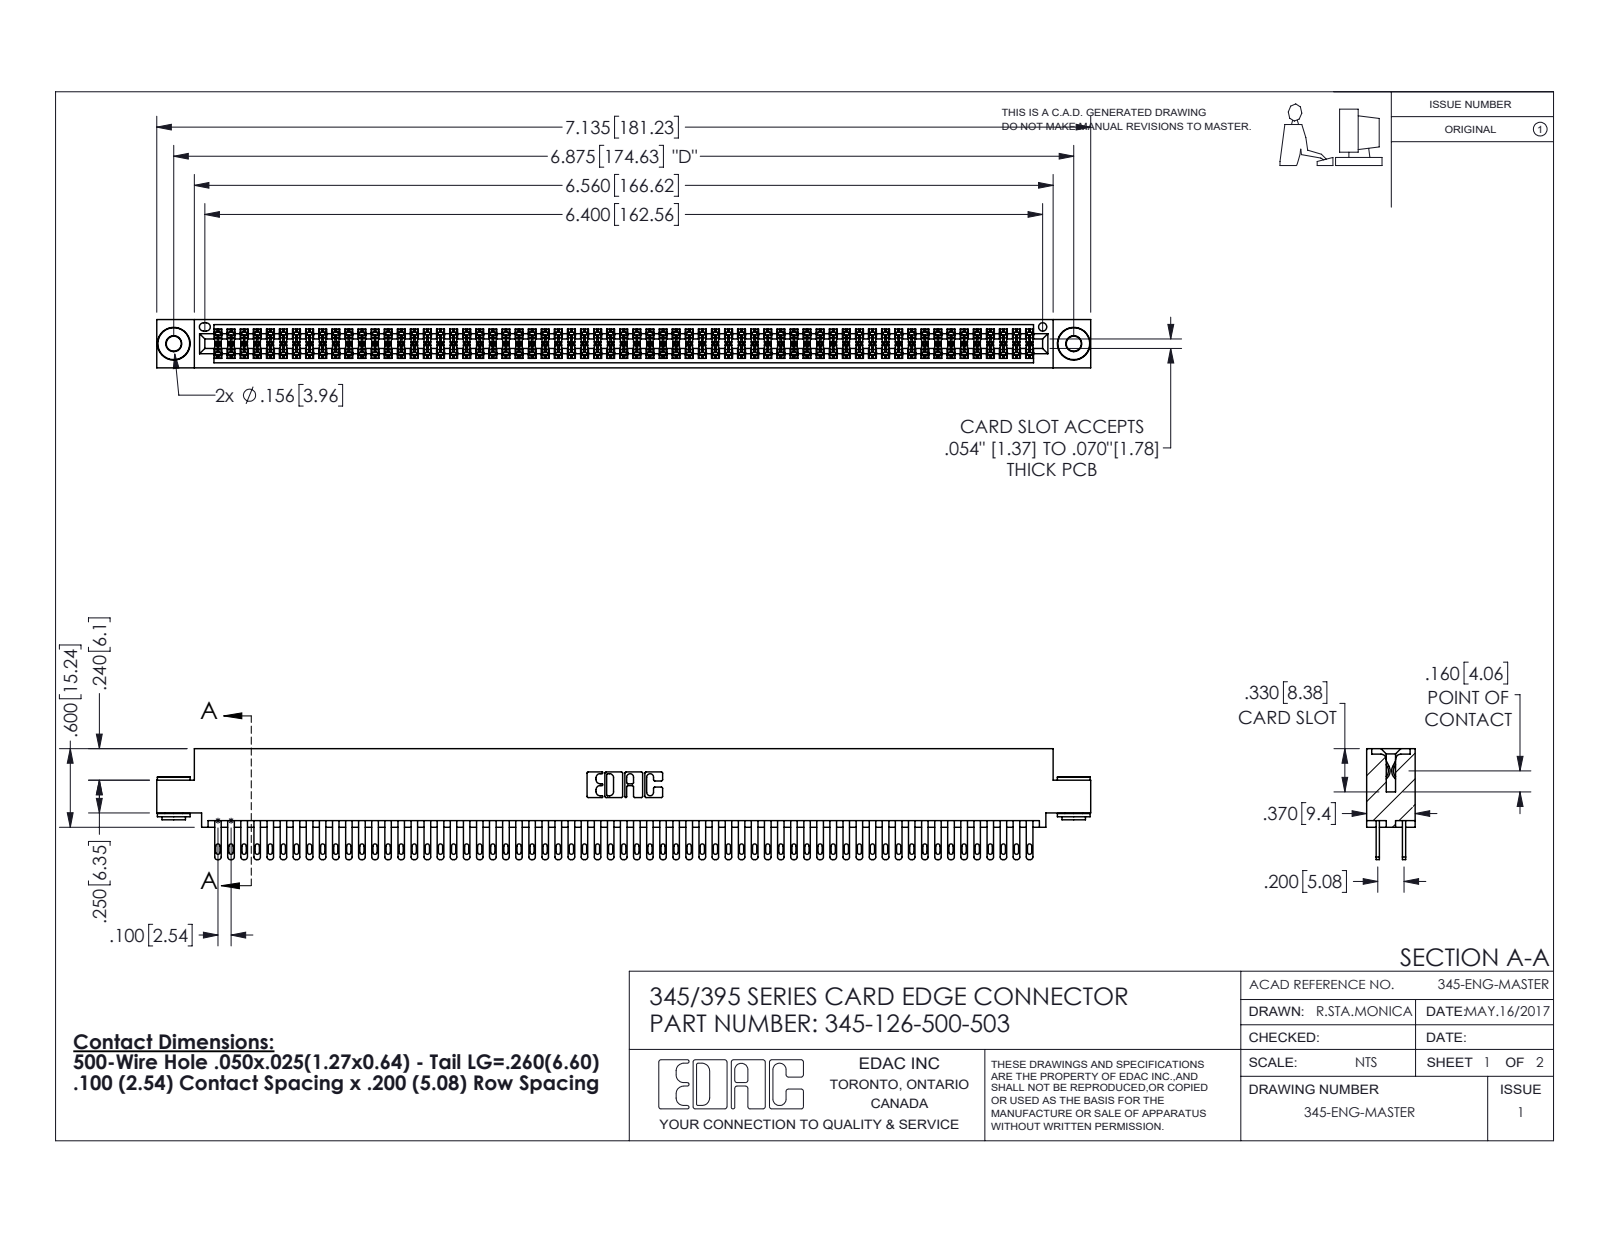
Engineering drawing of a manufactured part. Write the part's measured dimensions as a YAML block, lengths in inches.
part_name: "345-292-001_345-293-100; 345-250-002_345-250-002-102; 345-126-500-503; 345 Part_0.110 Offset - 0.156 Dia-TH"
step_written_by: "SolidWorks 2016 (CONFIG_CONTROL_DESIGN)"
units: inches
bodies: {solids: 129, faces: 5964, planar: 3496, cylindrical: 2460, other: 8}
overall_size: [7.135, 0.847, 0.37]
volume: 1.106
surface_area: 44.62
round_holes:
  - {diameter: 0.116, count: 2}
  - {diameter: 0.156, count: 2}
  - {diameter: 0.064, count: 1}
round_bosses_or_shafts:
  - {diameter: 0.25, count: 2}
  - {diameter: 0.18, count: 2}
  - {diameter: 0.136, count: 2}
partial_cylinders:
  - {radius: 0.006, count: 189}
  - {radius: 0.016, count: 126}
  - {radius: 0.02, count: 126}
  - {radius: 0.01, count: 22}
  - {radius: 0.007, count: 6}
  - {radius: 0.031, count: 6}
  - {radius: 0.026, count: 3}
  - {radius: 0.014, count: 2}
face_to_face_distances: [0.072, 0.298, 0.2, 0.025, 0.098, 0.272, 0.37, 0.225, 0.175, 0.149]
hole_center_spacings: [0.27, 6.639, 6.875]
